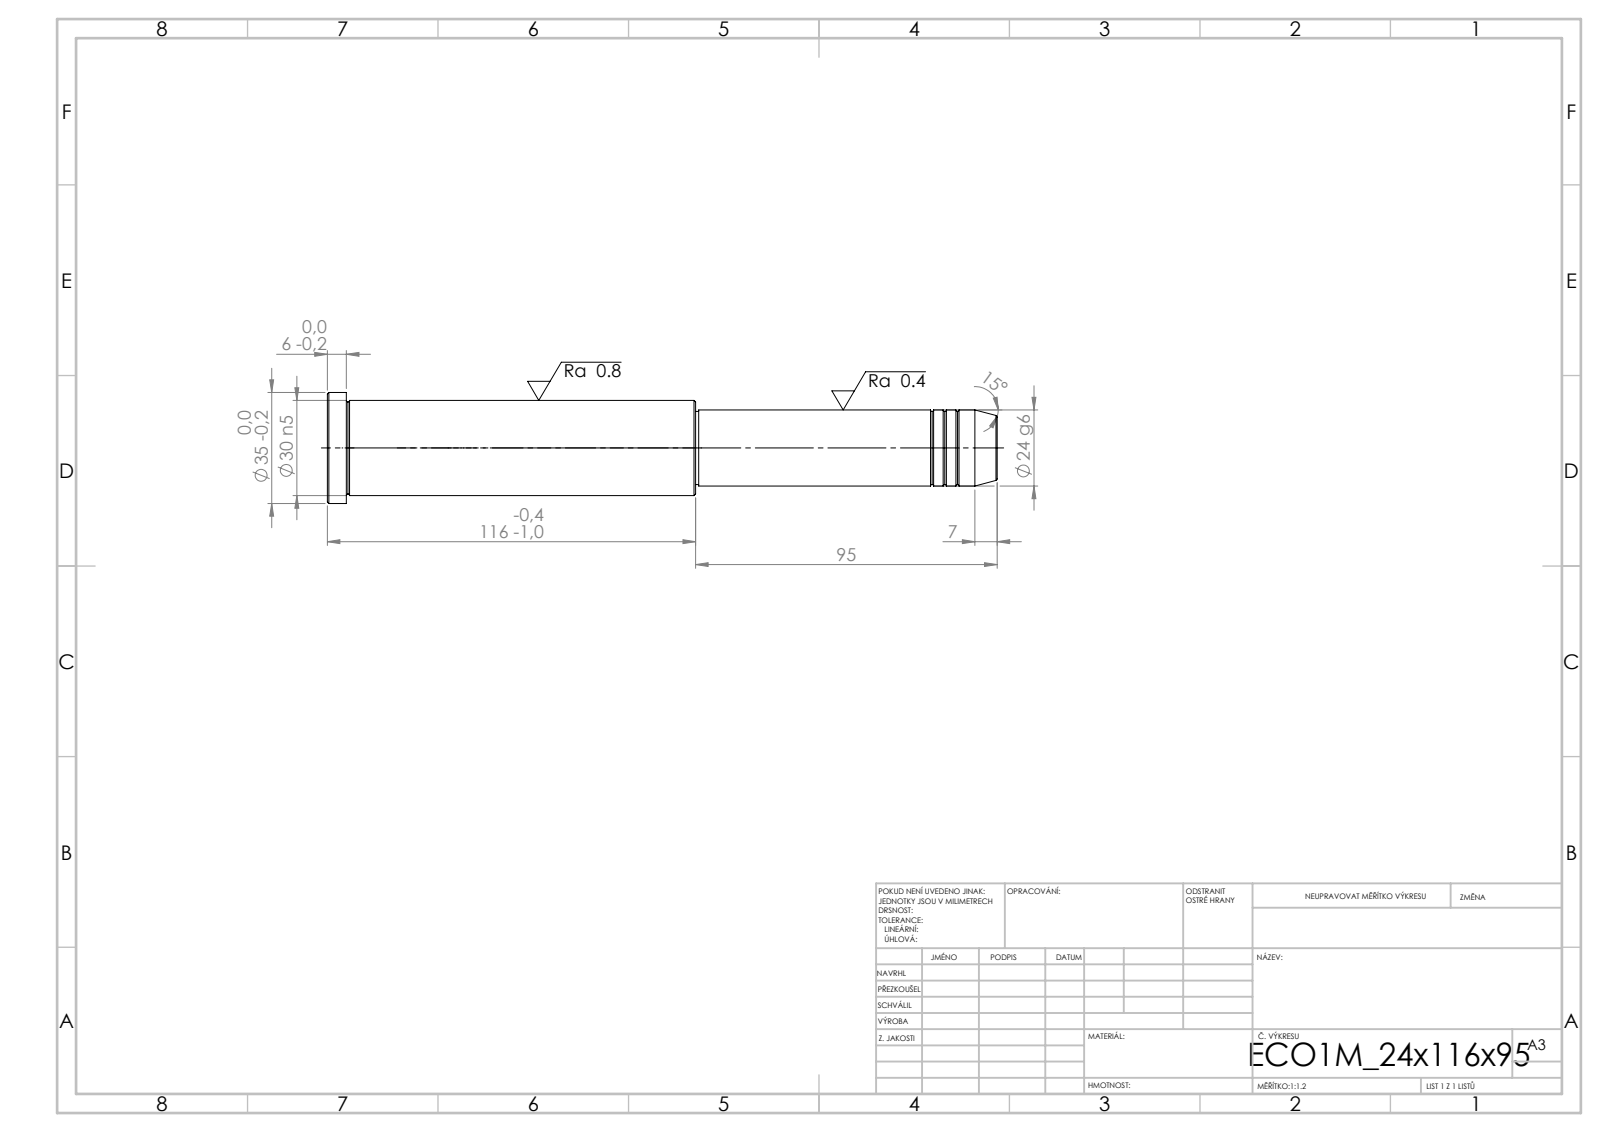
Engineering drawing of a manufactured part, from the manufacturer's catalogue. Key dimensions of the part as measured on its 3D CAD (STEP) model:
STEP written by: SolidWorks 2019 (CONFIG_CONTROL_DESIGN)
Units: millimetres
Bodies: 1 solid, 43 faces (5 planar, 14 cylindrical, 24 other)
Overall size (bounding box): 211 × 35 × 35
Volume: 125 847 mm³ · Surface area: 20 133 mm²
Round bosses / shafts (diameter × count): ⌀35 ×1, ⌀30 ×1, ⌀24 ×1, ⌀23 ×1
Main face-to-face distances: 211, 205, 6, 95, 110, 116, 94, 1, 111, 117
